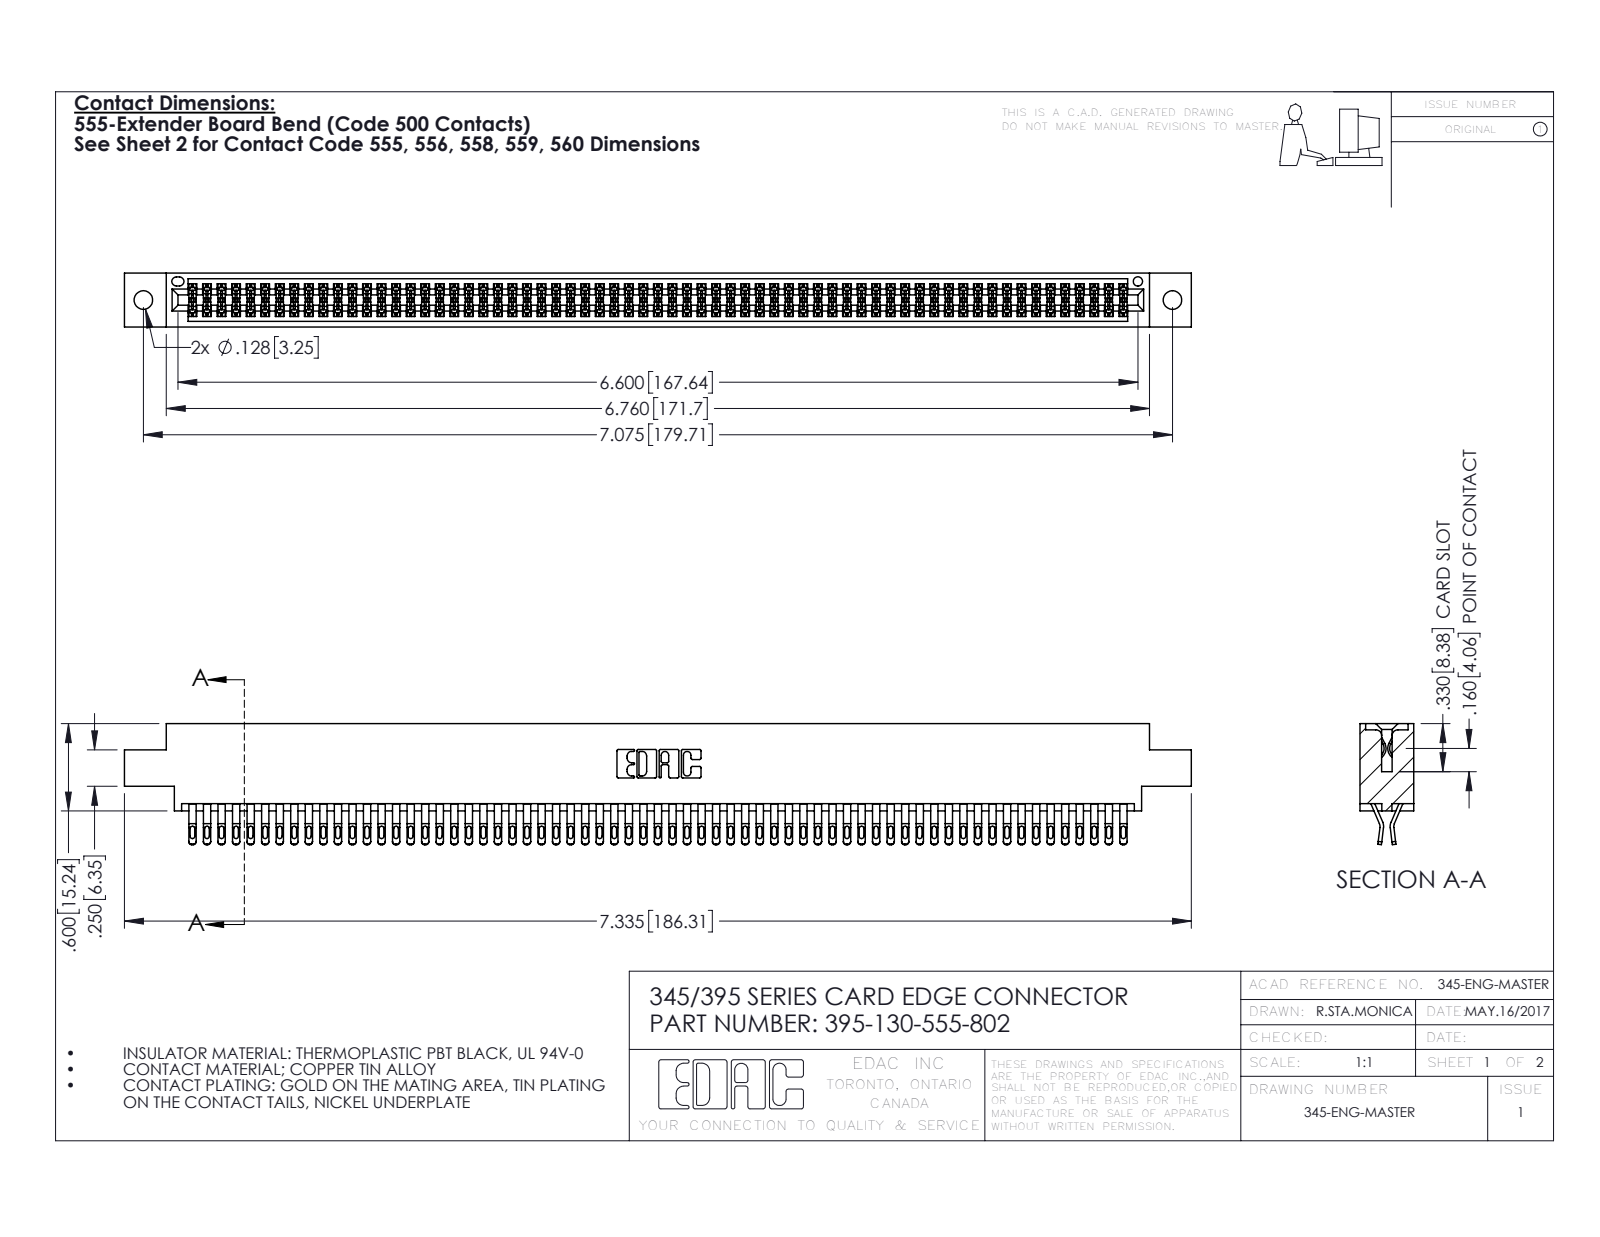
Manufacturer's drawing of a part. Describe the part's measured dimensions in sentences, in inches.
The part is named "395-130-555-802; 345-292-001_555 Tail; 345 Part_0.170 Offset - 0.128 Dia". Its 3-D file was written by "SolidWorks 2016 (CONFIG_CONTROL_DESIGN)". It is 131 solids with 7410 faces: 4114 planar, 3296 cylindrical and 0 other. Overall it measures 7.335 by 0.832 by 0.37 inches. Its volume is 1.133 cubic inches and its surface area 44.97 square inches. Round holes: 2 of diameter 0.128, 1 of diameter 0.064. Partial cylindrical surfaces (rounded edges, fillets, slot ends): 325 of radius 0.016, 260 of radius 0.02, 195 of radius 0.006, 22 of radius 0.01, 6 of radius 0.007, 6 of radius 0.031, 3 of radius 0.026, 2 of radius 0.01. The main face-to-face distances are 0.298, 0.072, 0.025, 0.37, 0.2, 0.098, 0.272, 0.225, 0.175, 0.149. The hole center spacings are 0.27, 6.839, 7.075.
